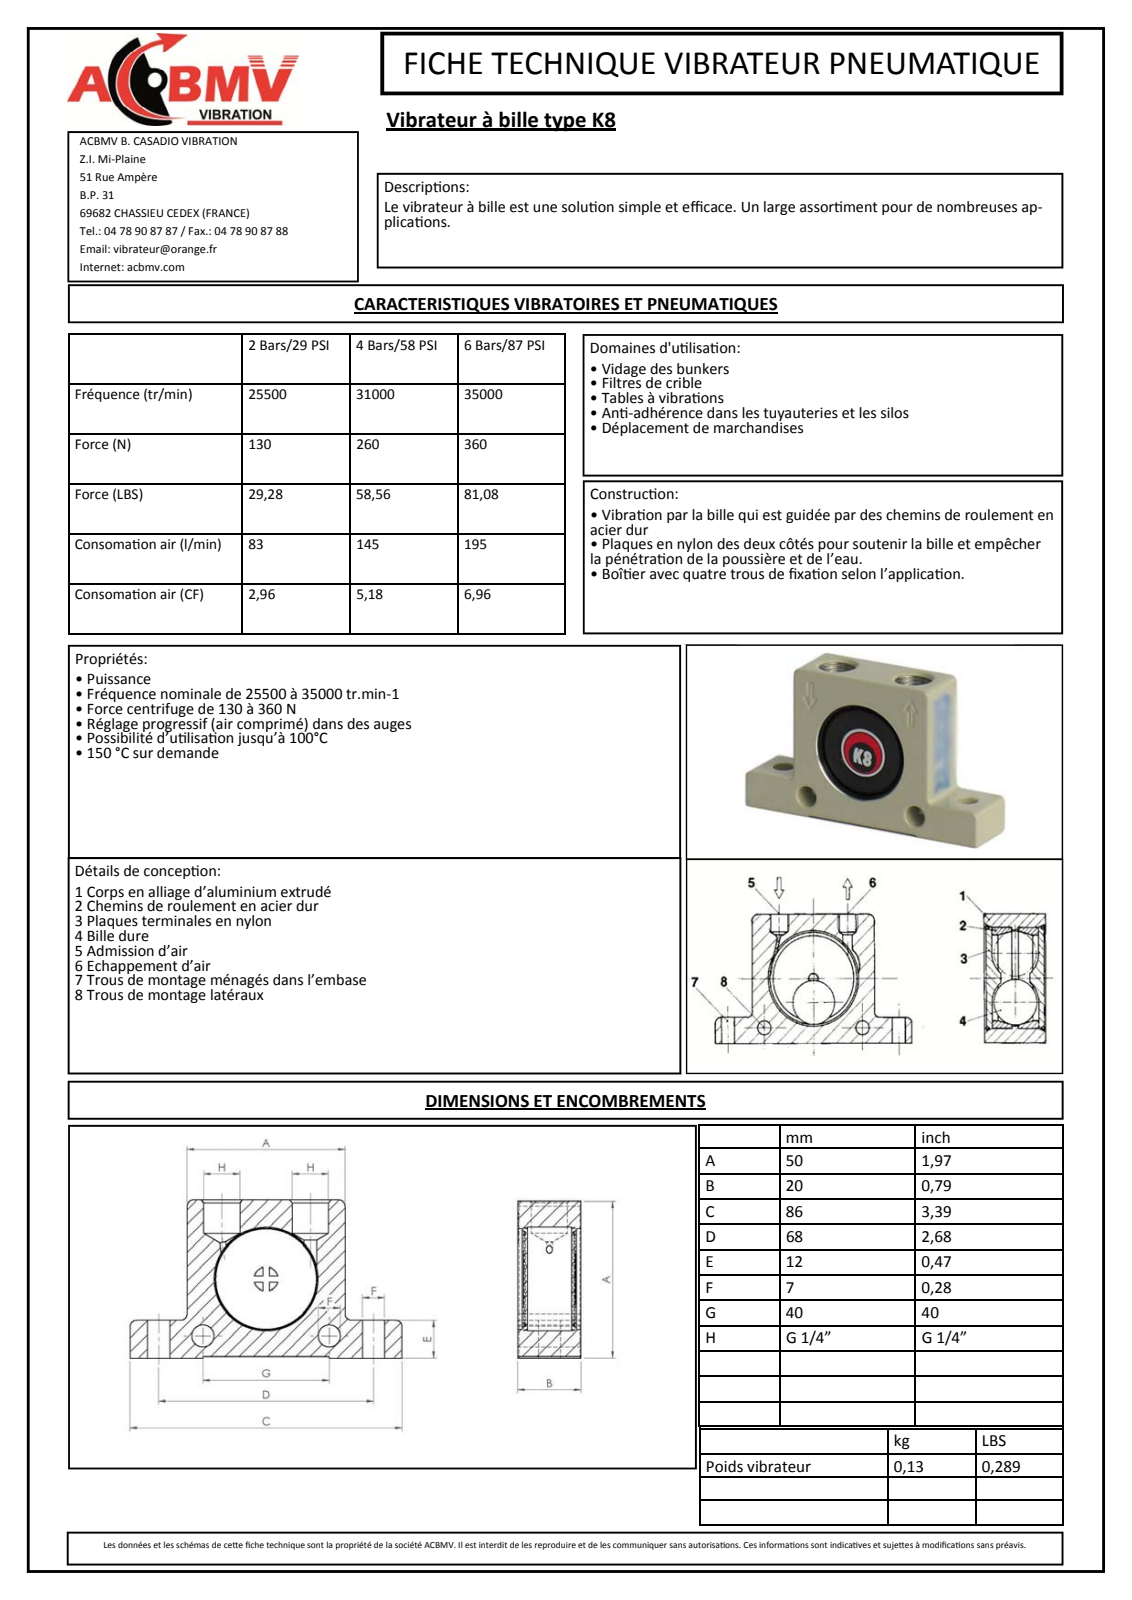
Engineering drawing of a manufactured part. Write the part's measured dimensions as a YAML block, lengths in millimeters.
part_name: "1008-00-M"
step_written_by: "Autodesk Inventor 2011 (CONFIG_CONTROL_DESIGN)"
units: millimeters
bodies: {solids: 1, faces: 356, planar: 214, cylindrical: 98, other: 44}
overall_size: [86, 50, 20]
volume: 38569
surface_area: 17528
round_holes:
  - {diameter: 7, count: 4}
  - {diameter: 11.45, count: 2}
  - {diameter: 1.67, count: 1}
  - {diameter: 1.9, count: 1}
  - {diameter: 4, count: 1}
  - {diameter: 10.5, count: 1}
  - {diameter: 14.5, count: 1}
  - {diameter: 17.5, count: 1}
  - {diameter: 31.9, count: 1}
  - {diameter: 32.9, count: 1}
round_bosses_or_shafts:
  - {diameter: 28, count: 1}
  - {diameter: 16, count: 1}
  - {diameter: 13.7, count: 1}
  - {diameter: 1.5, count: 1}
partial_cylinders:
  - {radius: 0.3, count: 14}
  - {radius: 7.88, count: 8}
  - {radius: 2, count: 6}
  - {radius: 0.43, count: 4}
  - {radius: 1.25, count: 4}
  - {radius: 1.55, count: 4}
  - {radius: 1.8, count: 4}
  - {radius: 10, count: 4}
face_to_face_distances: [20, 3, 17, 50, 0.5, 1.4, 18.6, 1.6, 15.6, 14]
hole_center_spacings: [20, 26.06, 26.91, 48, 1.3, 28, 40, 68]
